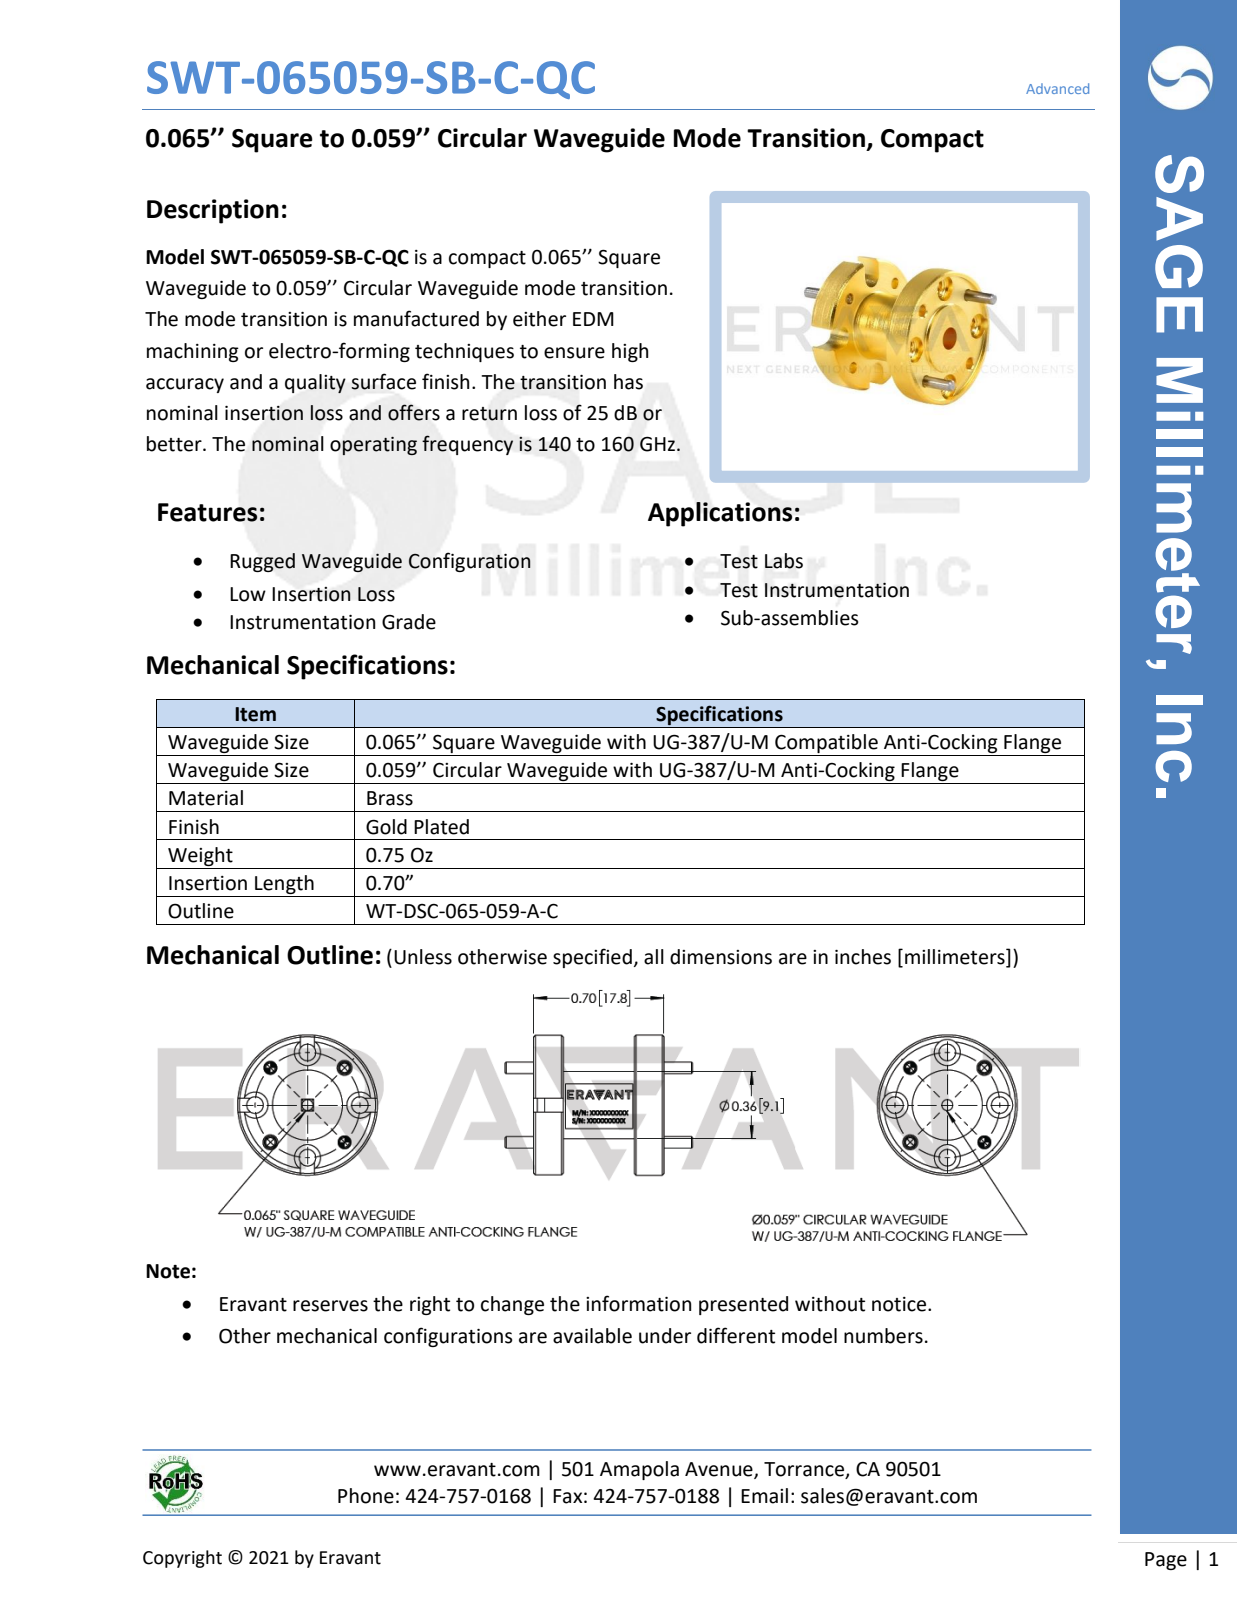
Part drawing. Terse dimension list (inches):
name: WT-DSC-065-059-A-C, Defeatured
written by: SolidWorks 2021 (AUTOMOTIVE_DESIGN)
unit: in
bodies: 5 solids, 175 faces (45 planar, 78 cylindrical, 52 other)
size: 1.005 × 0.75 × 0.75
volume: 0.157 in³; area: 3.444 in²
holes: 4× ⌀0.061, 4× ⌀0.067, 4× ⌀0.089, 4× ⌀0.14, 1× ⌀0.68
bosses: 4× ⌀0.063, 1× ⌀0.75, 1× ⌀0.375, 1× ⌀0.36
face distances: 0.14, 0.52, 0.02, 0.16, 0.54, 0.68, 0.38, 0.66, 0.7, 0.06
hole spacings: 0.215, 0.281, 0.398, 0.519, 0.562
